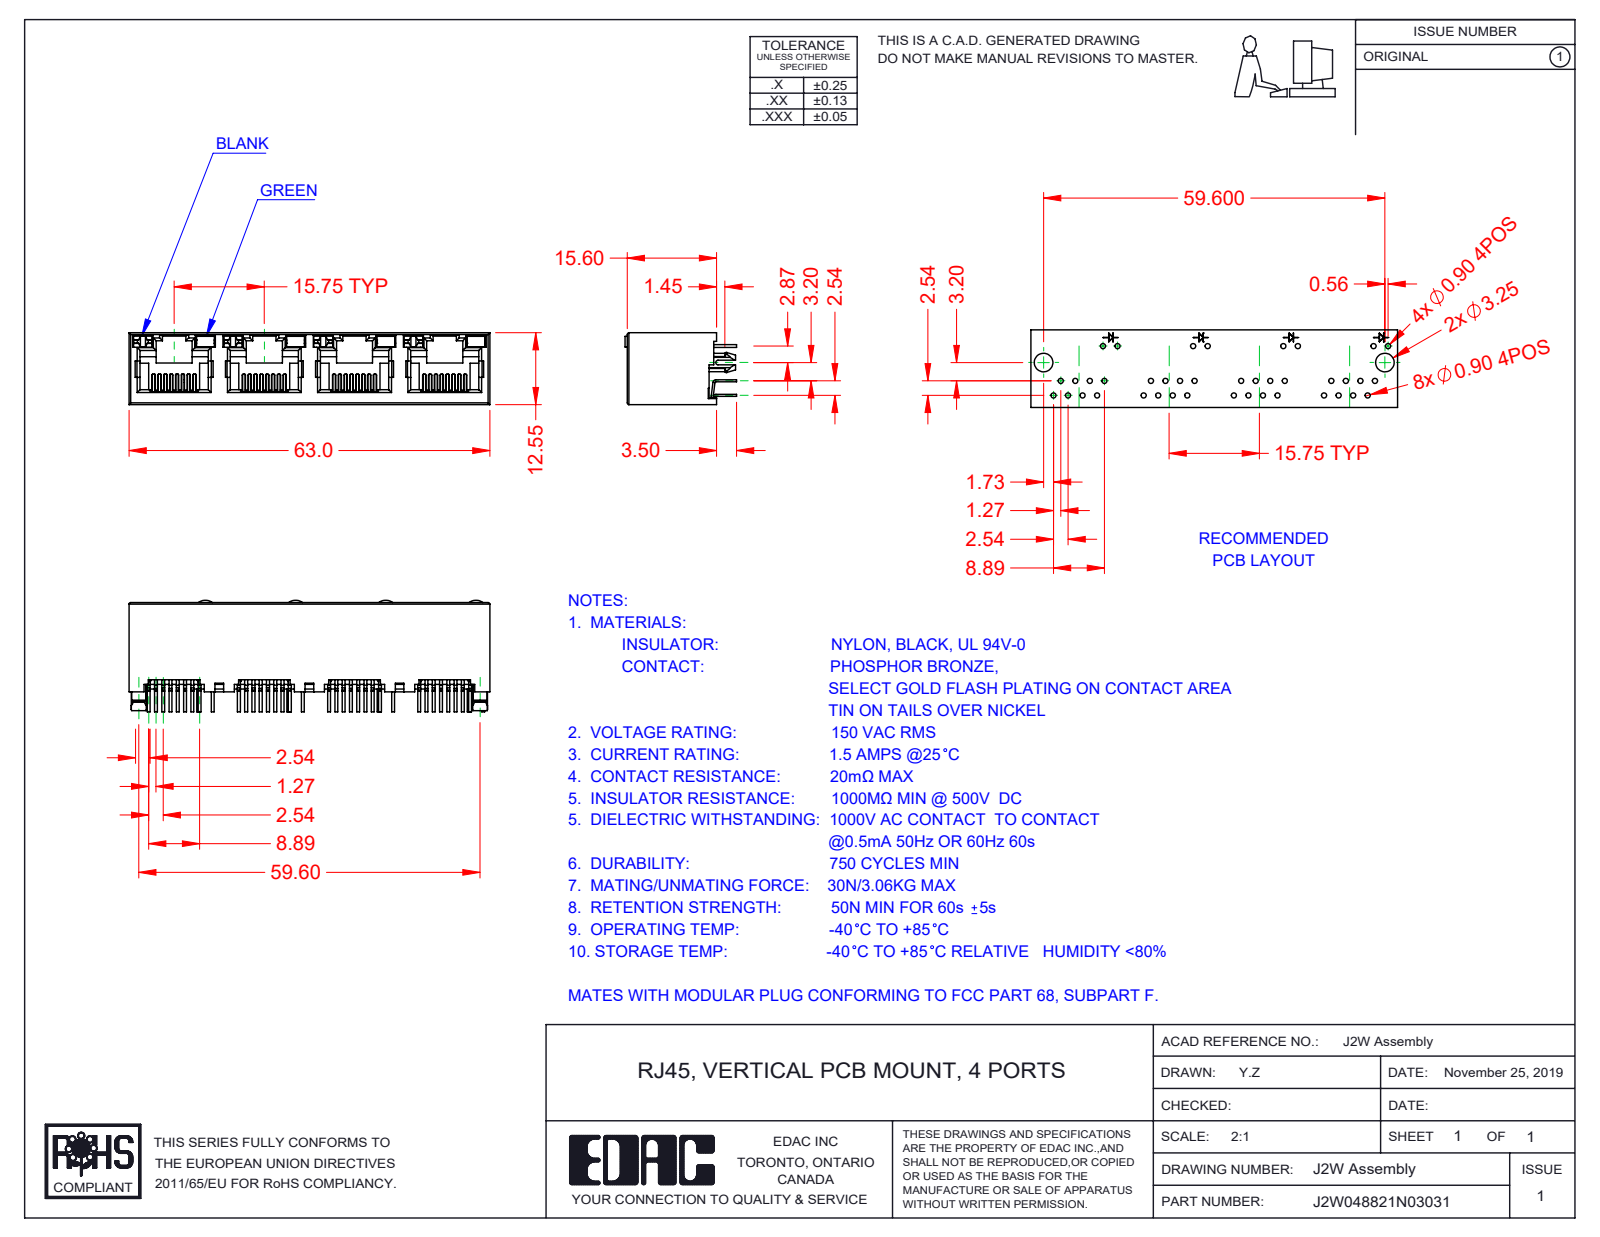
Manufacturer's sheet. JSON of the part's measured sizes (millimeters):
{"part_name": "J2W048821N03031; 2W Contacts; 2W LED LH_0-Blank; 2W LED RH_3-Green (+2 more)", "step_written_by": "SolidWorks 2020 (CONFIG_CONTROL_DESIGN)", "units": "millimeters", "bodies": {"solids": 41, "faces": 3007, "planar": 2508, "cylindrical": 441, "other": 58}, "overall_size": [63, 19.5, 12.55], "volume_mm3": 5212, "surface_area_mm2": 12695, "partial_cylinders_radius": [[0.15, 64], [0.2, 29], [0.5, 28], [0.3, 14], [0.45, 8], [2, 4], [0.25, 2], [1.5, 2]], "face_to_face_distances": [12.55, 11.9, 0.65, 15.75, 0.36, 1.5, 0.78, 0.6, 11.3, 31.5]}
